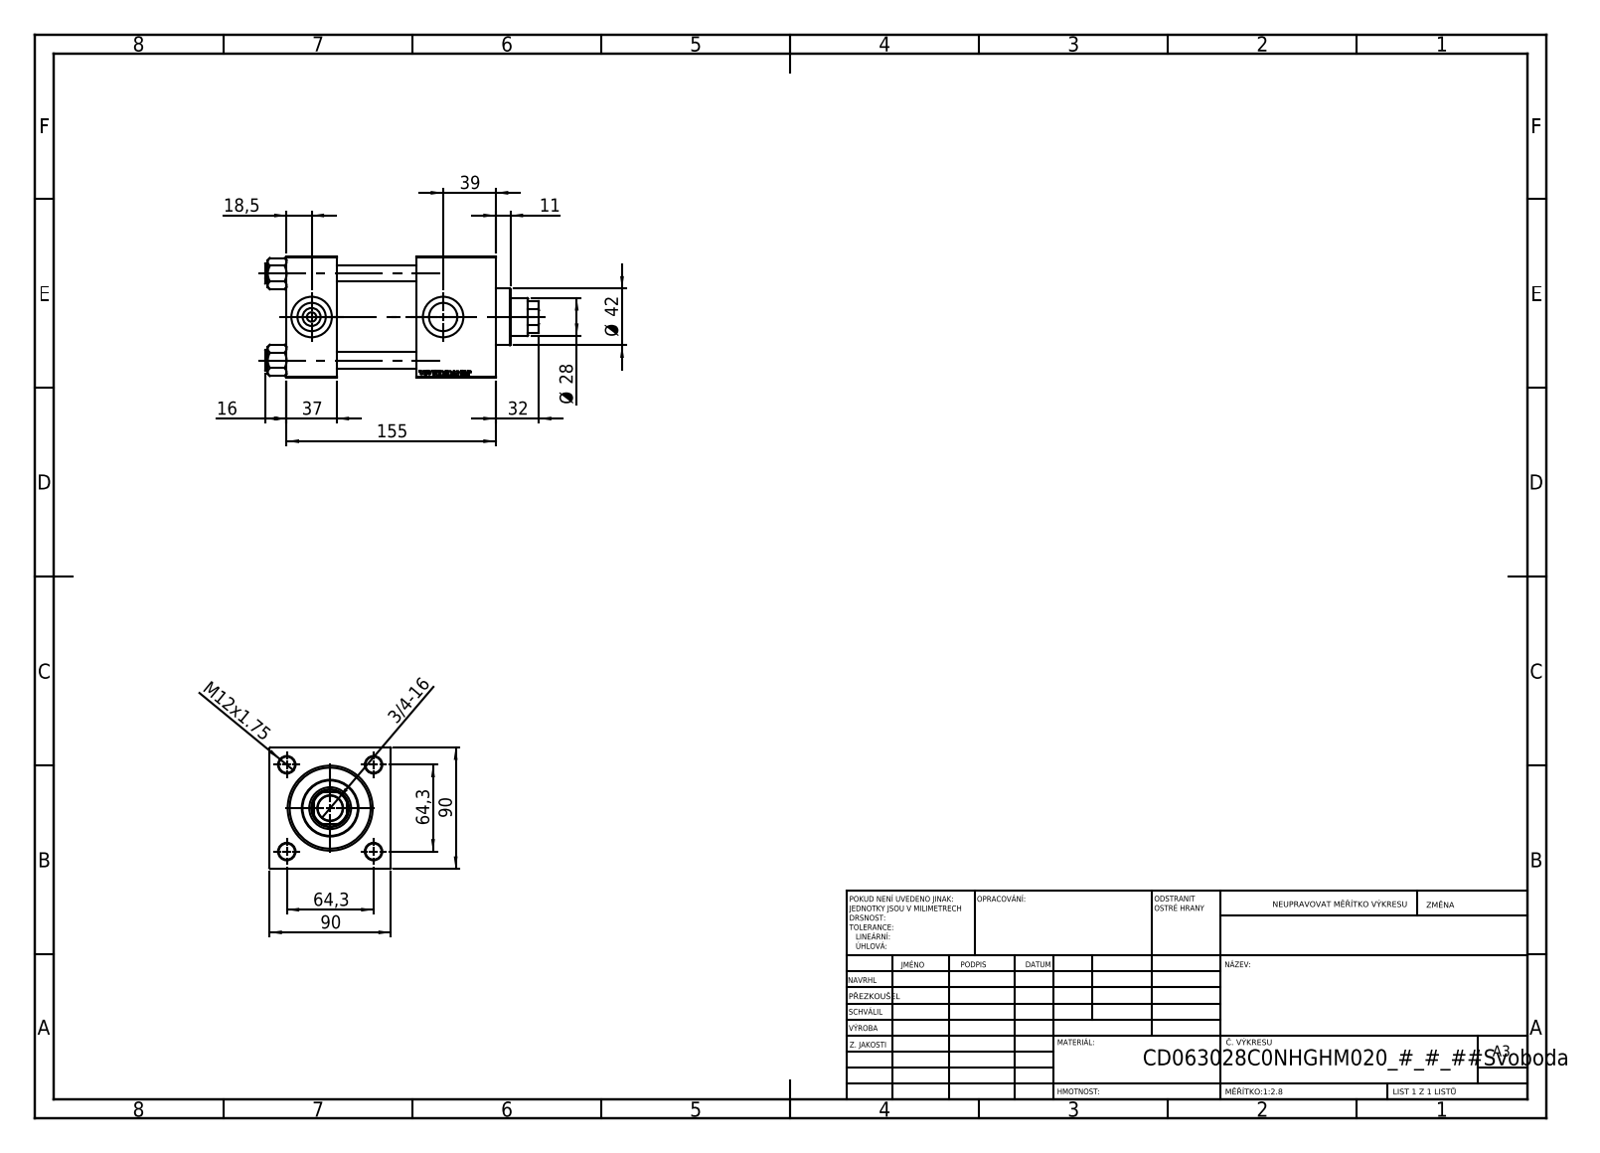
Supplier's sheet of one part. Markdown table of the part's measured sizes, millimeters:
| quantity | value |
| --- | --- |
| part name | NUT_M5_V215CD_C; V215CD_VC_C; V215CD_VCP_C; V215CD_C_TYCINKA (+1 more) |
| STEP written by | SolidWorks 2019 (CONFIG_CONTROL_DESIGN) |
| units | millimeters |
| bodies | 11 solids, 1148 faces (526 planar, 86 cylindrical, 536 other) |
| overall size | 203 × 90 × 90 |
| volume | 946 885 mm³ |
| surface area | 179 128 mm² |
| round holes (diameter × count) | 12 × 4, 7 × 2, 20.96 × 2, 30 × 2, 18.5 × 1, 28 × 1, 31 × 1, 50 × 1, 60 × 1, 63 × 1 |
| round bosses / shafts (diameter × count) | 15 × 4, 69 × 1, 42 × 1 |
| partial cylindrical surfaces (radius × count) | 13.5 × 1 |
| main face-to-face distances | 90, 59, 37, 155, 118, 96, 126.3, 89.3, 30.3, 28.7 |
| hole center spacings | 45.47, 64.3, 90.93, 97.5 |
